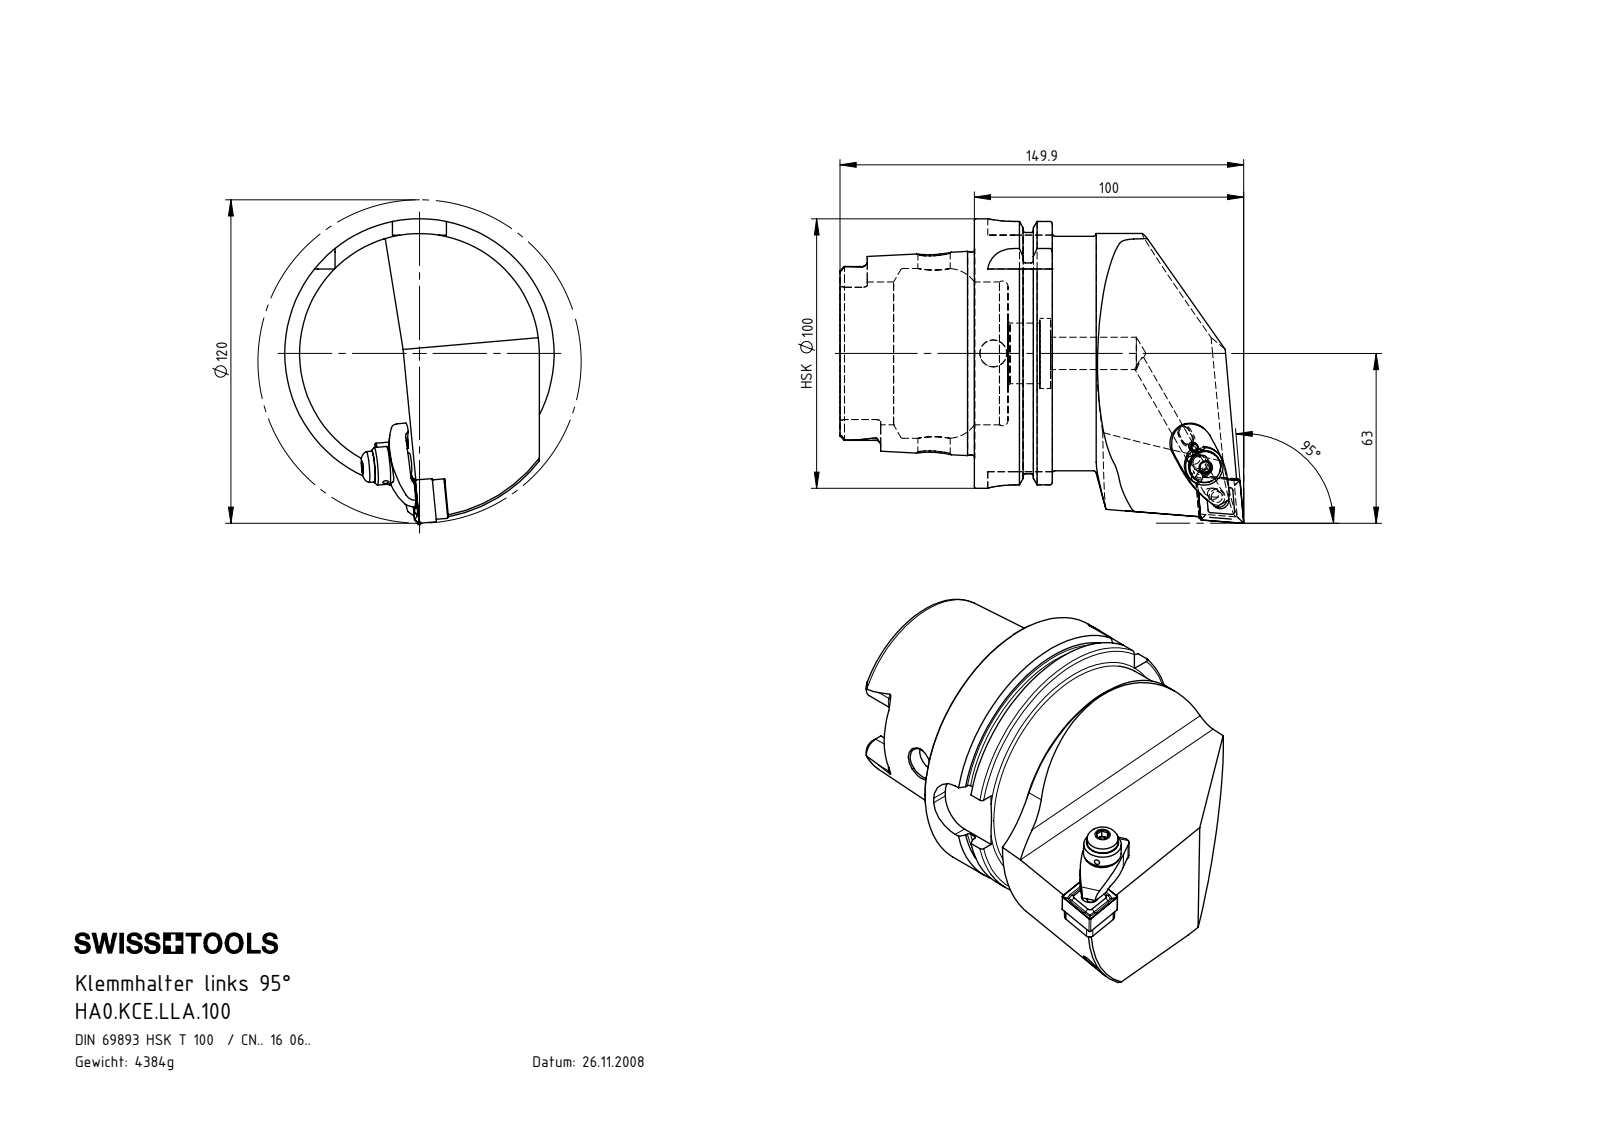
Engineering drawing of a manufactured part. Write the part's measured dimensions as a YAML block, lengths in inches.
part_name: "WCE-ER2.001.012_A; HA0.KCE.LLA.100; KVT_MB_600_060; CNMG160604 (+7 more)"
step_written_by: "SolidWorks 2017 (AUTOMOTIVE_DESIGN)"
units: inches
bodies: {solids: 11, faces: 343, planar: 122, cylindrical: 102, other: 119}
overall_size: [5.902, 4.449, 3.937]
volume: 31.92
surface_area: 113.9
round_holes:
  - {diameter: 0.079, count: 3}
  - {diameter: 0.197, count: 3}
  - {diameter: 0.165, count: 2}
  - {diameter: 0.276, count: 2}
  - {diameter: 0.472, count: 2}
  - {diameter: 0.094, count: 1}
  - {diameter: 0.118, count: 1}
  - {diameter: 0.236, count: 1}
  - {diameter: 0.244, count: 1}
  - {diameter: 0.25, count: 1}
  - {diameter: 0.317, count: 1}
  - {diameter: 0.335, count: 1}
round_bosses_or_shafts:
  - {diameter: 0.236, count: 2}
  - {diameter: 0.118, count: 2}
  - {diameter: 3.937, count: 1}
  - {diameter: 3.62, count: 1}
  - {diameter: 3.425, count: 1}
  - {diameter: 2.963, count: 1}
  - {diameter: 0.551, count: 1}
  - {diameter: 0.453, count: 1}
partial_cylinders:
  - {radius: 0.059, count: 7}
  - {radius: 0.018, count: 6}
  - {radius: 0.075, count: 6}
  - {radius: 0.016, count: 4}
  - {radius: 0.031, count: 4}
  - {radius: 0.394, count: 4}
  - {radius: 0.031, count: 2}
  - {radius: 0.079, count: 2}
face_to_face_distances: [0.49, 0.65, 1.14, 1.965, 2.455, 3.104, 3.457, 0.026, 3.079, 1.114]
hole_center_spacings: [0.315, 0.323, 0.538, 0.922, 0.929, 0.236, 0.243, 0.417]
